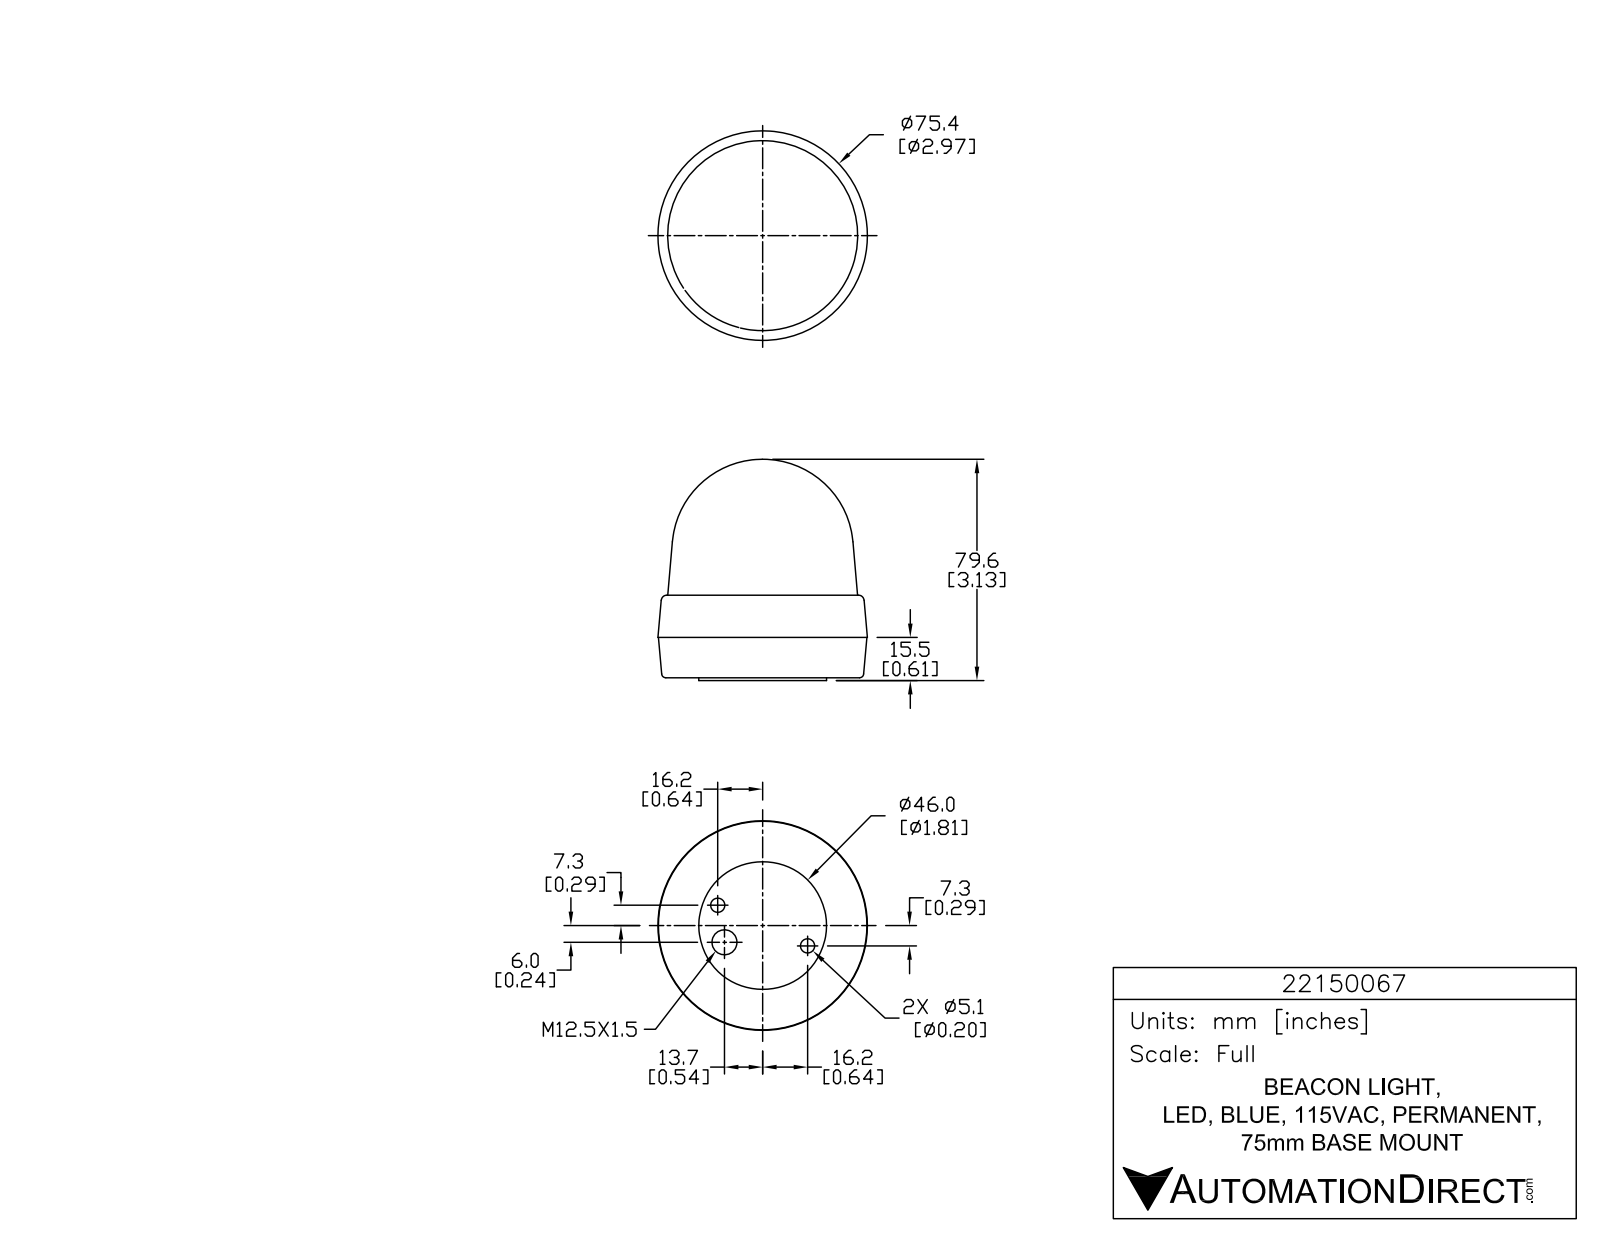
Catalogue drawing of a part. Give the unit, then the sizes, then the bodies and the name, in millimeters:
Units: millimetres
Overall size (bounding box): 79.6 × 75.4 × 75.4
Round holes (diameter × count): ⌀1.5 ×3, ⌀5.1 ×2, ⌀9 ×1
Round bosses / shafts (diameter × count): ⌀8.6 ×3, ⌀2.1 ×3, ⌀46 ×1
Partial cylindrical surfaces — rounded edges, fillets, slot ends (radius × count): R0.1 ×9, R0.1 ×6, R0.3 ×6, R0.3 ×6, R0.3 ×6, R5 ×6, R0.1 ×3, R0.1 ×3
Main face-to-face distances: 1, 30.7, 29.7, 15.5, 14.5, 15.2, 39.8, 38.8, 24.3, 9.1
Hole centre spacings: 13.6, 29.9, 35.5
Volume: 258 800 mm³ · Surface area: 21 740 mm²
Bodies: 1 solid, 773 faces (526 planar, 163 cylindrical, 84 other)
Part name (STEP PRODUCT): 22150067
STEP written by: SolidWorks 2015 (AUTOMOTIVE_DESIGN)
